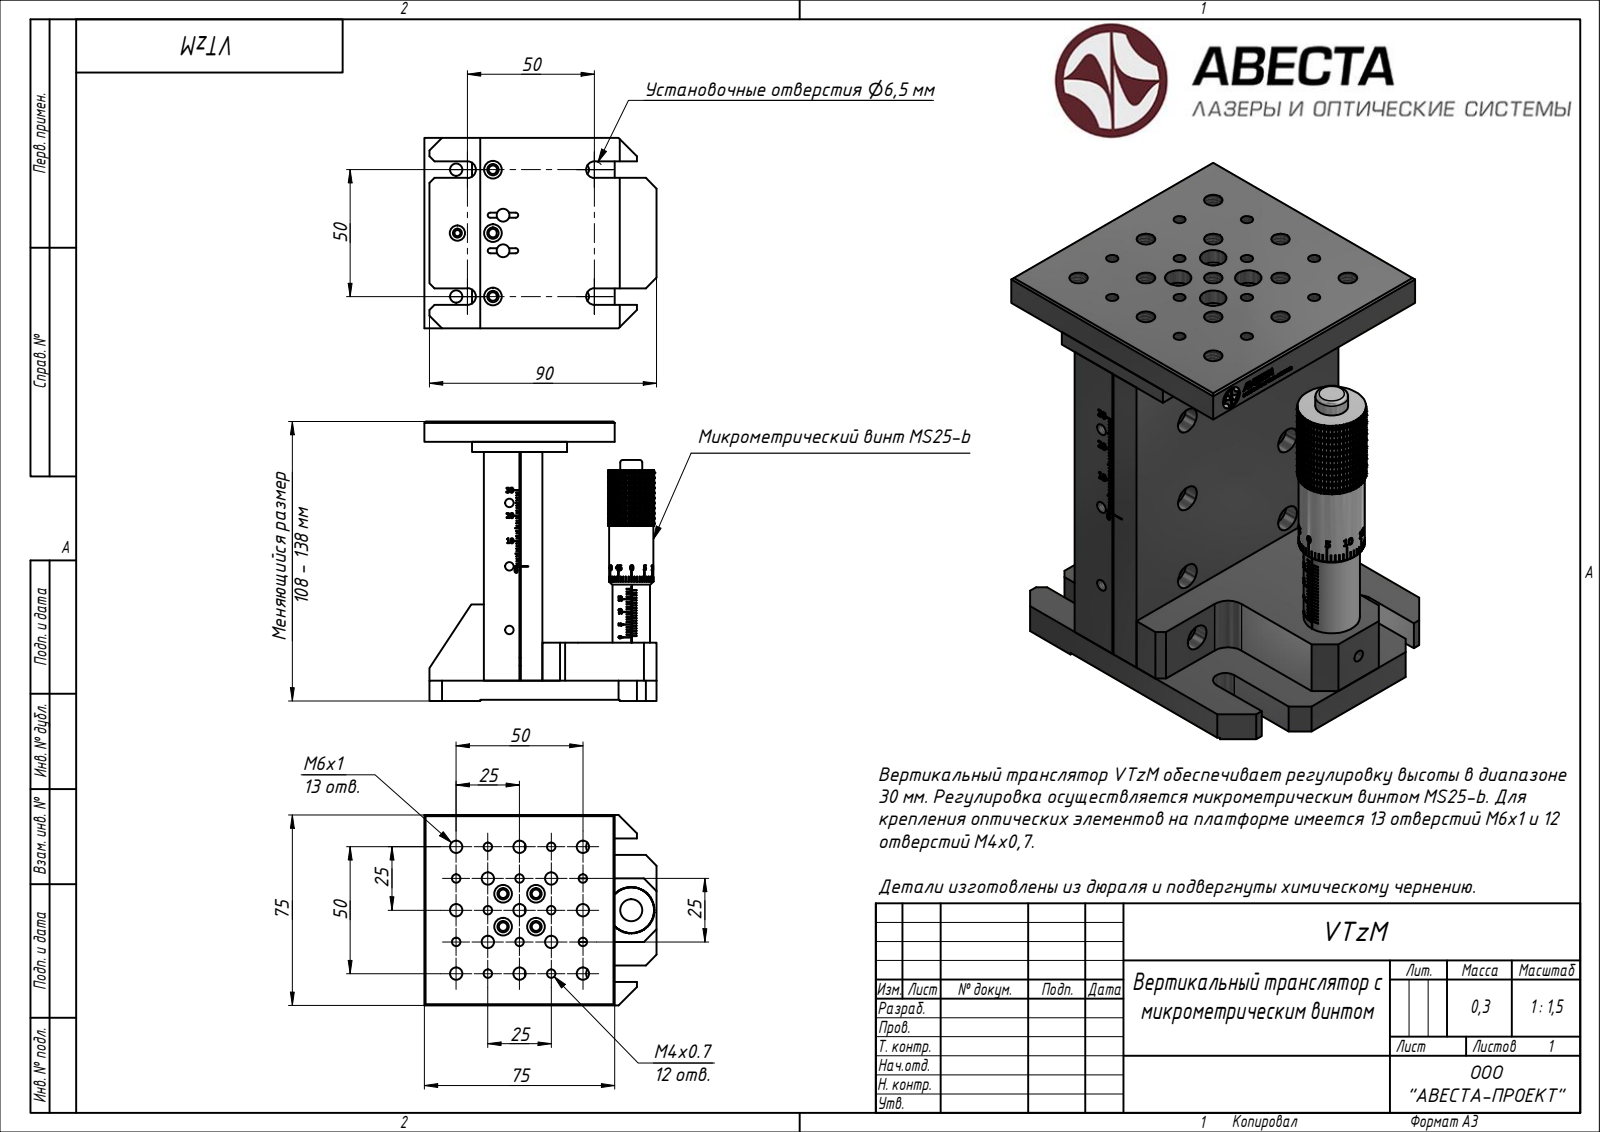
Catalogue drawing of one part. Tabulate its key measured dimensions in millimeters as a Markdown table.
| quantity | value |
| --- | --- |
| STEP written by | Rhino 7.34 (AUTOMOTIVE_DESIGN) |
| units | millimeters |
| bodies | 618 solids, 6907 faces (5813 planar, 482 cylindrical, 612 other) |
| overall size | 110 × 91.5 × 75 |
| volume | 268 278 mm³ |
| surface area | 86 479 mm² |
| round holes (diameter × count) | 3.24 × 37, 4.5 × 21, 7 × 21, 6 × 19, 4.92 × 13, 2.46 × 10, 3.5 × 10, 5.5 × 3, 5 × 2, 1.57 × 1, 6.5 × 1, 8 × 1 |
| round bosses / shafts (diameter × count) | 18 × 1, 17.4 × 1, 14.8 × 1, 8.66 × 1 |
| partial cylindrical surfaces (radius × count) | 1 × 4, 3.25 × 4, 5 × 3, 0.18 × 1, 0.45 × 1, 0.52 × 1, 0.78 × 1, 0.78 × 1 |
| main face-to-face distances | 23, 8, 5, 9, 75, 18, 8.5, 102, 17, 0.5 |
| hole center spacings | 25, 39.53, 17.68, 27.95, 50, 12.5, 35.36, 47.1 |
